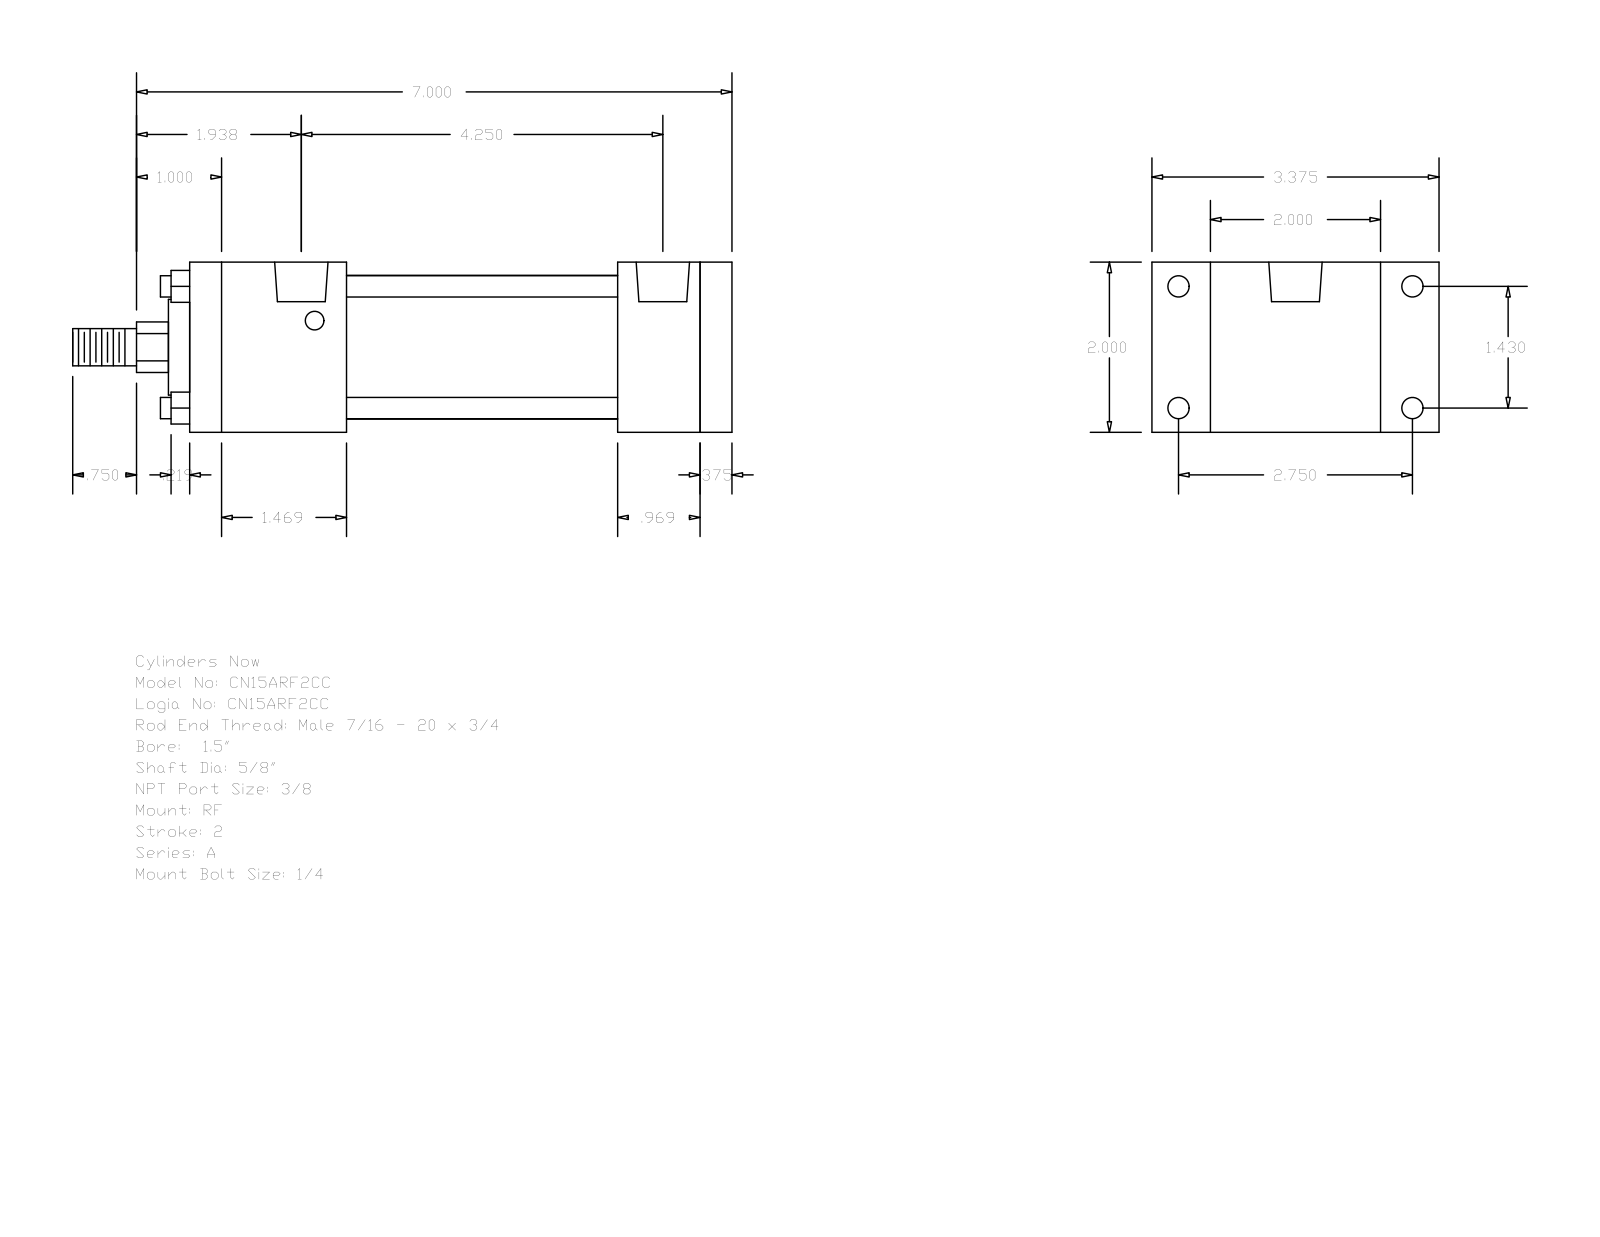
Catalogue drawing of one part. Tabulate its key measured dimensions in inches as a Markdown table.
| quantity | value |
| --- | --- |
| part name | A_RF__0150_0.625 |
| STEP written by | GSSL Pune (CONFIG_CONTROL_DESIGN) |
| units | inches |
| bodies | 0 solids, 92 faces (64 planar, 28 cylindrical, 0 other) |
| overall size | 7.75 × 3.375 × 2 |
| round holes (diameter × count) | 0.219 × 4, 0.25 × 4, 0.627 × 2 |
| round bosses / shafts (diameter × count) | 0.25 × 4, 1.69 × 1, 1.125 × 1, 0.625 × 1, 0.437 × 1 |
| partial cylindrical surfaces (radius × count) | 0.297 × 1 |
| main face-to-face distances | 2, 0.375, 6, 6.375, 5.031, 0.969, 1.344, 1.844, 3.187, 4.156 |
| hole center spacings | 0.156, 1.43, 2.75, 3.099, 3.937, 4.094, 4.25 |
